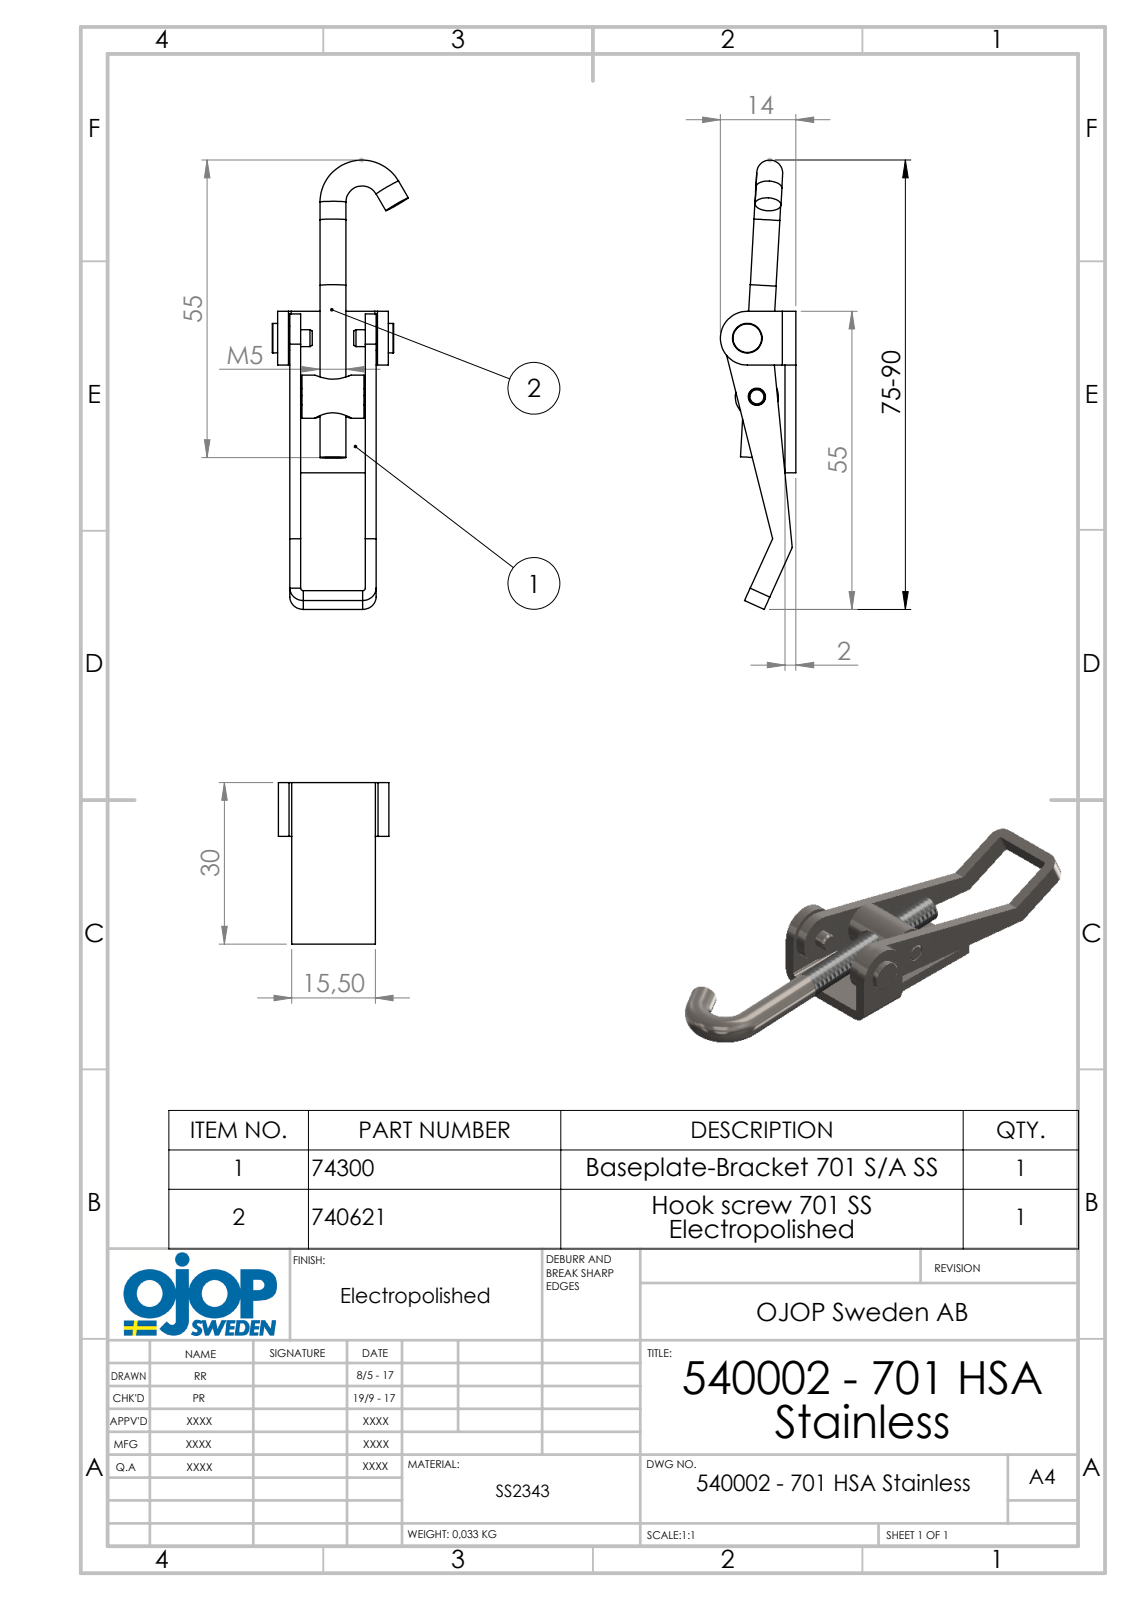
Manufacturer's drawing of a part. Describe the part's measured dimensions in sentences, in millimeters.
The part is named "701 - SA; 701 - Bygel; 701 - Ansatsnit; 701 - Mid Cylinder (+2 more)". Its 3-D file was written by "SolidWorks 2015 (AUTOMOTIVE_DESIGN)". It is 6 solids with 121 faces: 50 planar, 53 cylindrical and 18 other. Overall it measures 81.97 by 25.2 by 14 millimeters. Its volume is 4 512 cubic millimeters and its surface area 5 383 square millimeters. Round holes: 2 of diameter 3.2, 1 of diameter 4.5, 1 of diameter 4.8. Round bosses or shafts: 2 of diameter 4.8, 1 of diameter 8, 1 of diameter 5.5, 1 of diameter 4.81, 1 of diameter 3.15, 1 of diameter 3. Partial cylindrical surfaces (rounded edges, fillets, slot ends): 4 of radius 0.5, 4 of radius 2.5, 1 of radius 4.5, 1 of radius 5. The main face-to-face distances are 2, 14, 16, 2.25, 16.25, 12, 4.25, 18.25, 18.5, 14.25. The hole center spacings are 11.02.
